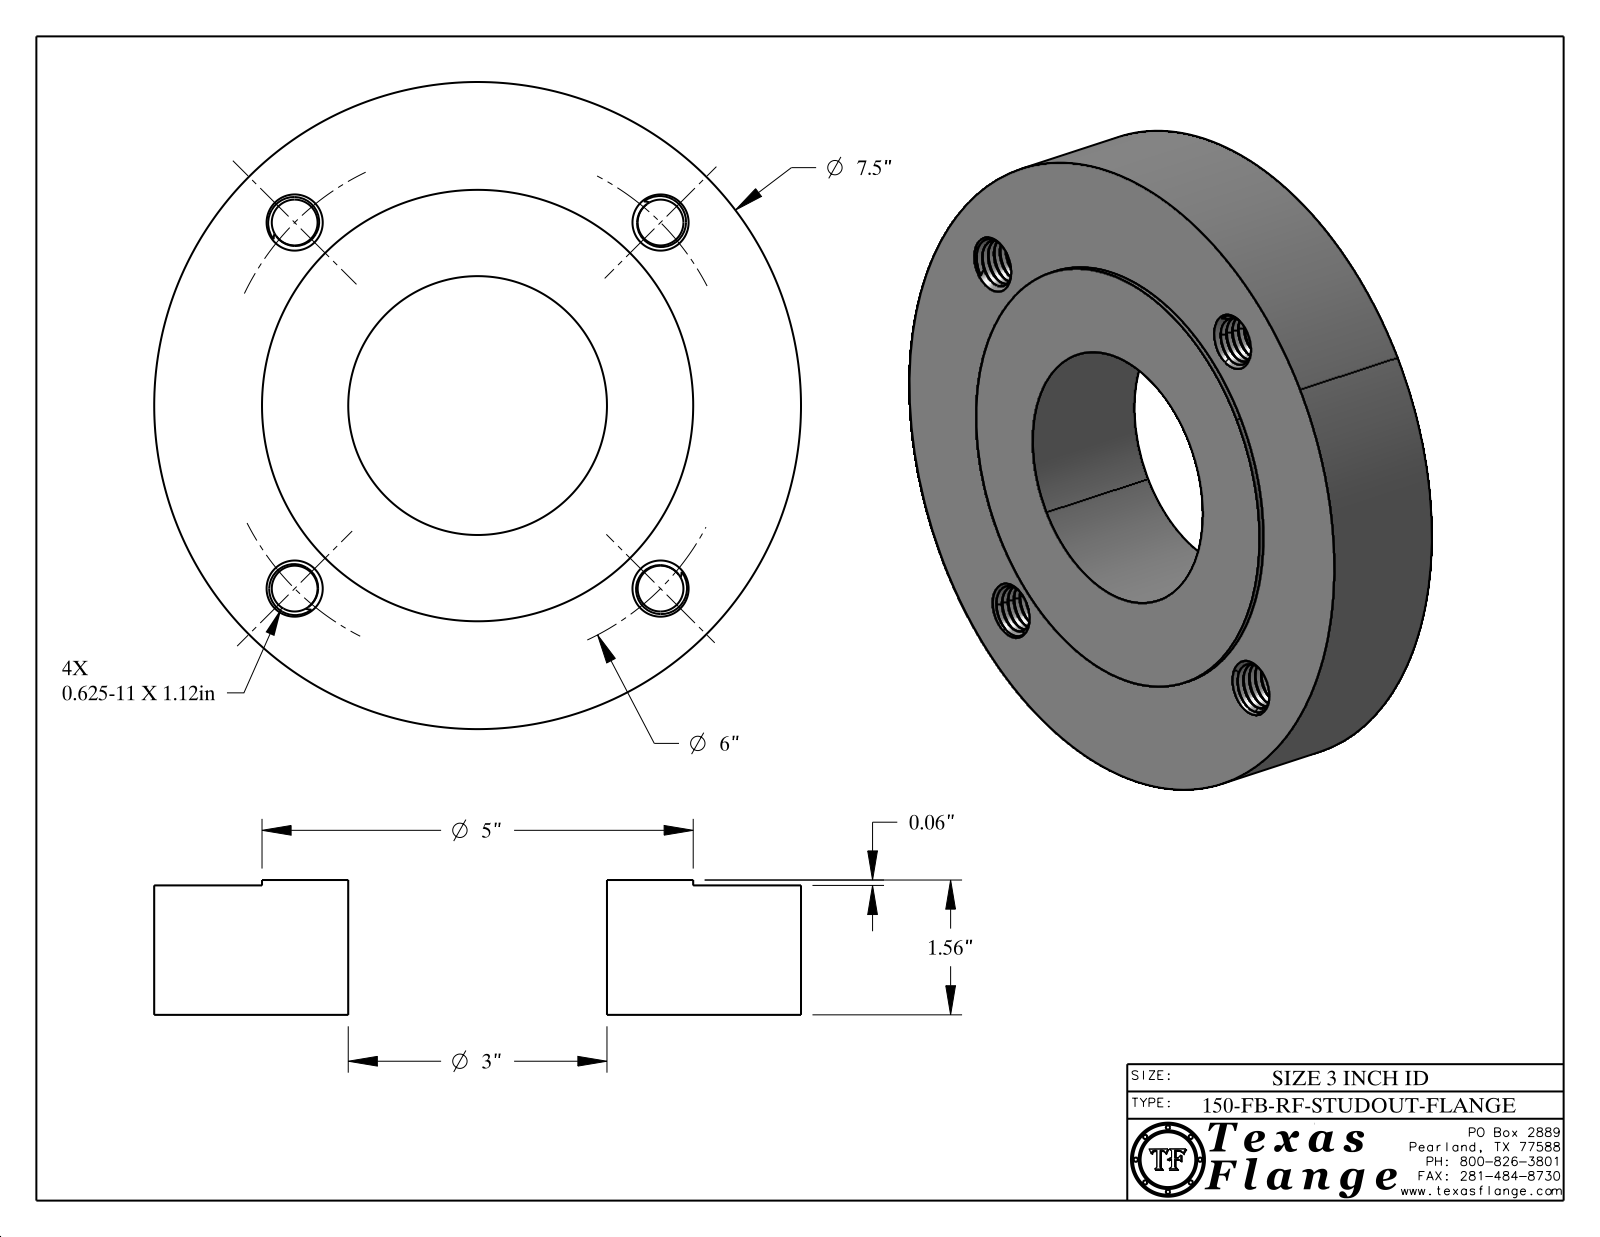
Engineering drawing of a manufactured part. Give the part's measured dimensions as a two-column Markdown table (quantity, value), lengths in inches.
| quantity | value |
| --- | --- |
| part name | 3-150-FB-RF-STUDOUT-FLANGE |
| STEP written by | CATIA V5 STEP AP214 (AUTOMOTIVE_DESIGN) |
| units | inches |
| bodies | 1 solid, 618 faces (368 planar, 98 cylindrical, 152 other) |
| overall size | 7.5 × 7.5 × 1.563 |
| volume | 55.29 in³ |
| surface area | 135.4 in² |
| round holes (diameter × count) | 0.531 × 4, 1 × 1, 3 × 1 |
| round bosses / shafts (diameter × count) | 0.061 × 8, 7.5 × 1, 5 × 1, 0.788 × 1 |
| main face-to-face distances | 1.5, 0.063, 1.563, 1.548, 1.485, 0.015, 0.298, 0.293, 0.054, 0.248 |
| hole center spacings | 3, 4.243, 2.296, 5.543, 6 |
